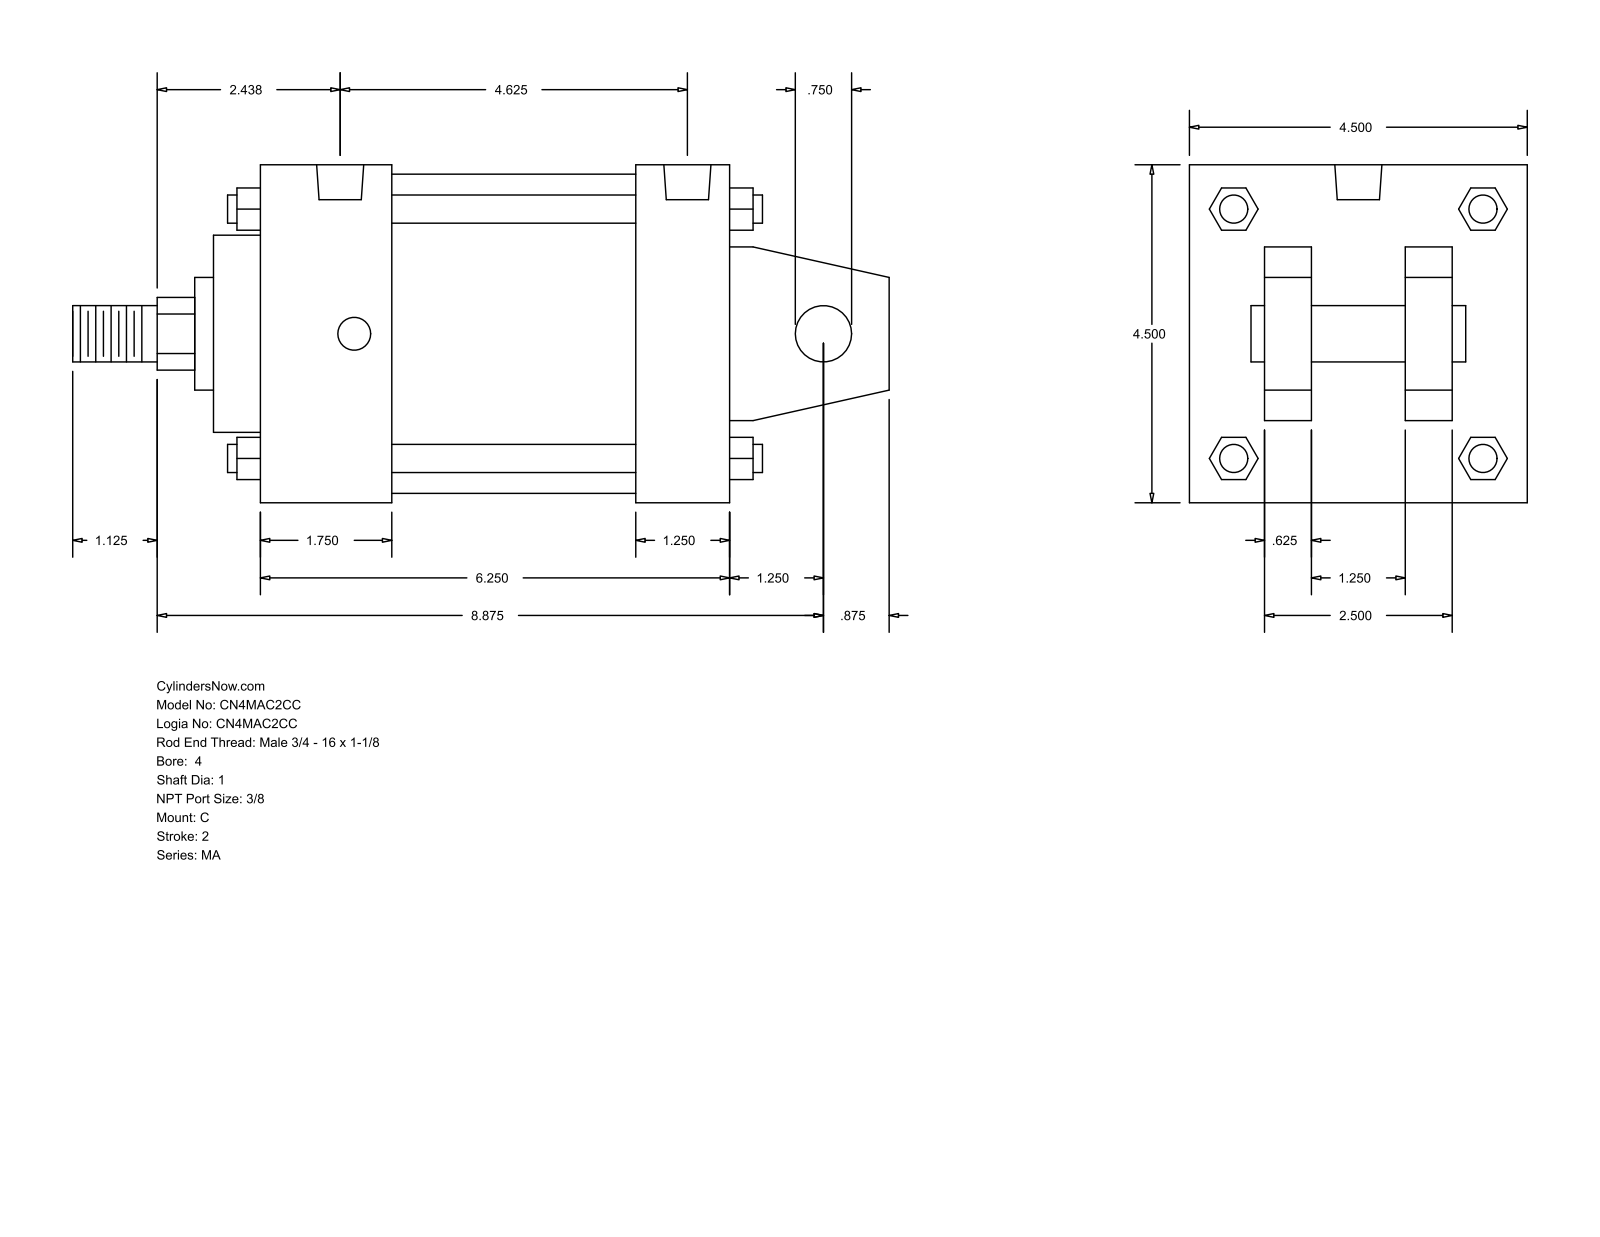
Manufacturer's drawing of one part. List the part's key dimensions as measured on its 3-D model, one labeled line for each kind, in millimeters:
Part name (STEP PRODUCT): MA_C__0400_1
STEP written by: GSSL Pune (CONFIG_CONTROL_DESIGN)
Units: millimetres
Bodies: 0 solids, 141 faces (109 planar, 32 cylindrical, 0 other)
Overall size (bounding box): 276.23 × 114.3 × 114.3
Round holes (diameter × count): ⌀11.11 ×4, ⌀15.93 ×2
Round bosses / shafts (diameter × count): ⌀9.53 ×4, ⌀19.05 ×2, ⌀107.95 ×1, ⌀66.67 ×1, ⌀38.1 ×1, ⌀25.4 ×1
Partial cylindrical surfaces — rounded edges, fillets, slot ends (radius × count): R12.29 ×1
Main face-to-face distances: 114.3, 158.76, 15.87, 73.03, 41.27, 25.4, 88.9, 47.63, 127.01, 31.75
Hole centre spacings: 107.95, 4.76, 4.77, 112.71, 112.72, 117.48
